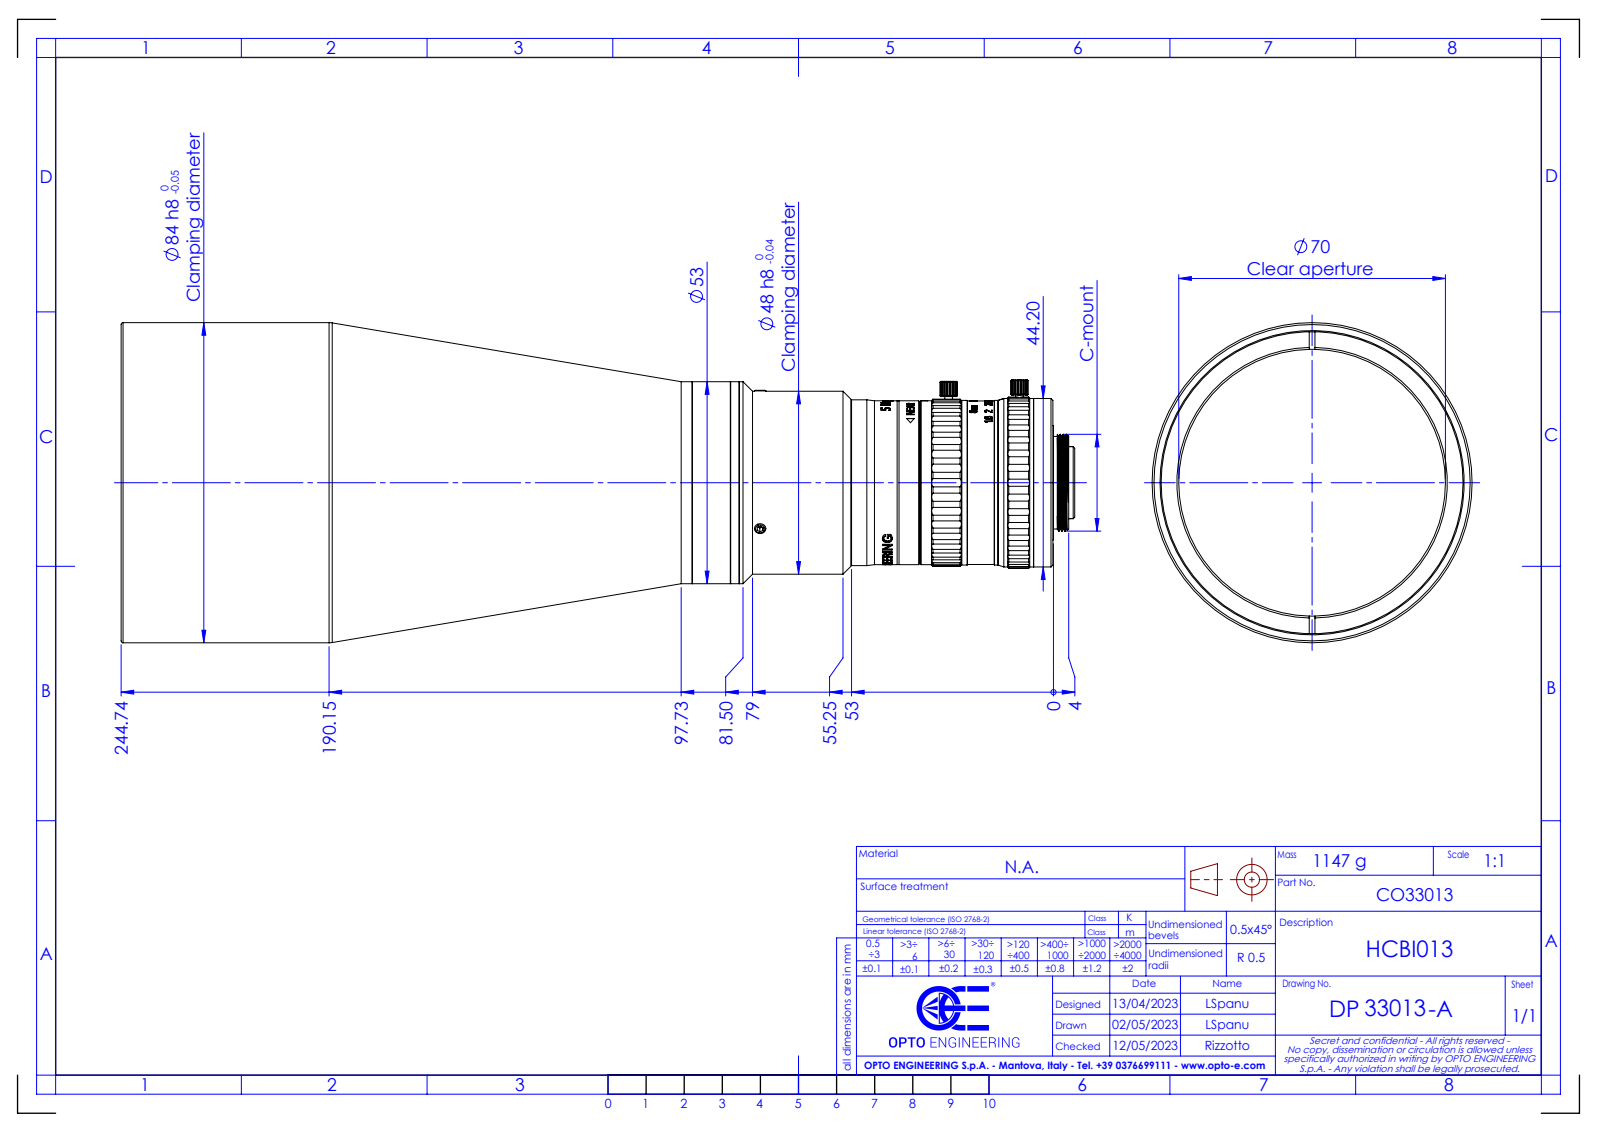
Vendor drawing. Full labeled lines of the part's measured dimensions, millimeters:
Part name (STEP PRODUCT): DP33013-A_HCBI013
STEP written by: SolidWorks 2021 (CONFIG_CONTROL_DESIGN)
Units: millimetres
Bodies: 0 solids, 526 faces (80 planar, 358 cylindrical, 88 other)
Overall size (bounding box): 250.31 × 84 × 84
Round holes (diameter × count): ⌀13.6 ×1, ⌀21.5 ×1, ⌀41.49 ×1, ⌀70 ×1, ⌀79.25 ×1
Round bosses / shafts (diameter × count): ⌀84 ×1, ⌀53 ×1, ⌀48 ×1, ⌀44.2 ×1, ⌀43.5 ×1, ⌀43.2 ×1, ⌀43 ×1, ⌀42.94 ×1
Partial cylindrical surfaces — rounded edges, fillets, slot ends (radius × count): R2 ×72, R2.25 ×2, R1 ×1, R21.33 ×1, R21.4 ×1, R21.95 ×1, R22.5 ×1
Main face-to-face distances: 2.75, 244.08, 241.33, 84.58, 159.5, 156.75, 0.51, 3.26, 160.01, 244.59
